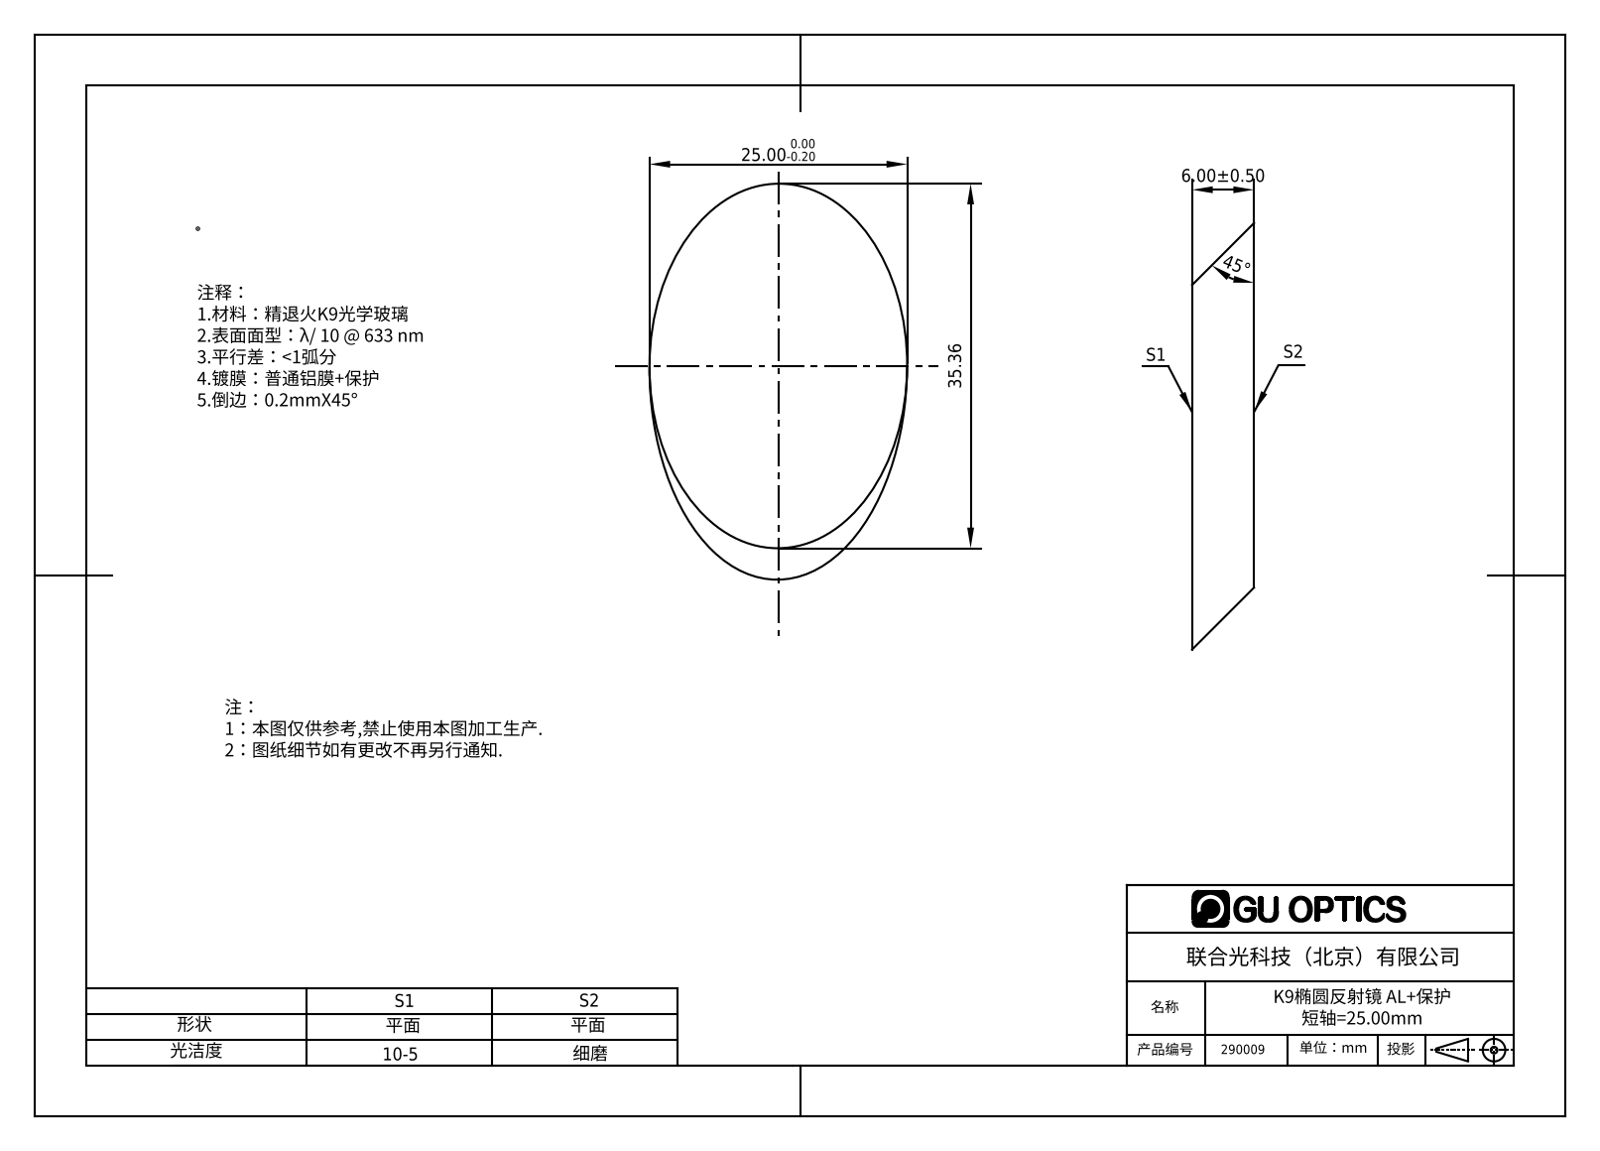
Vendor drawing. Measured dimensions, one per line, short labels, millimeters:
name: 290001
written by: SolidWorks 2016 (AUTOMOTIVE_DESIGN)
unit: mm
bodies: 1 solid, 4 faces (2 planar, 0 cylindrical, 2 other)
size: 41.36 × 25 × 6
volume: 4 166 mm³; area: 2 055 mm²
face distances: 6
